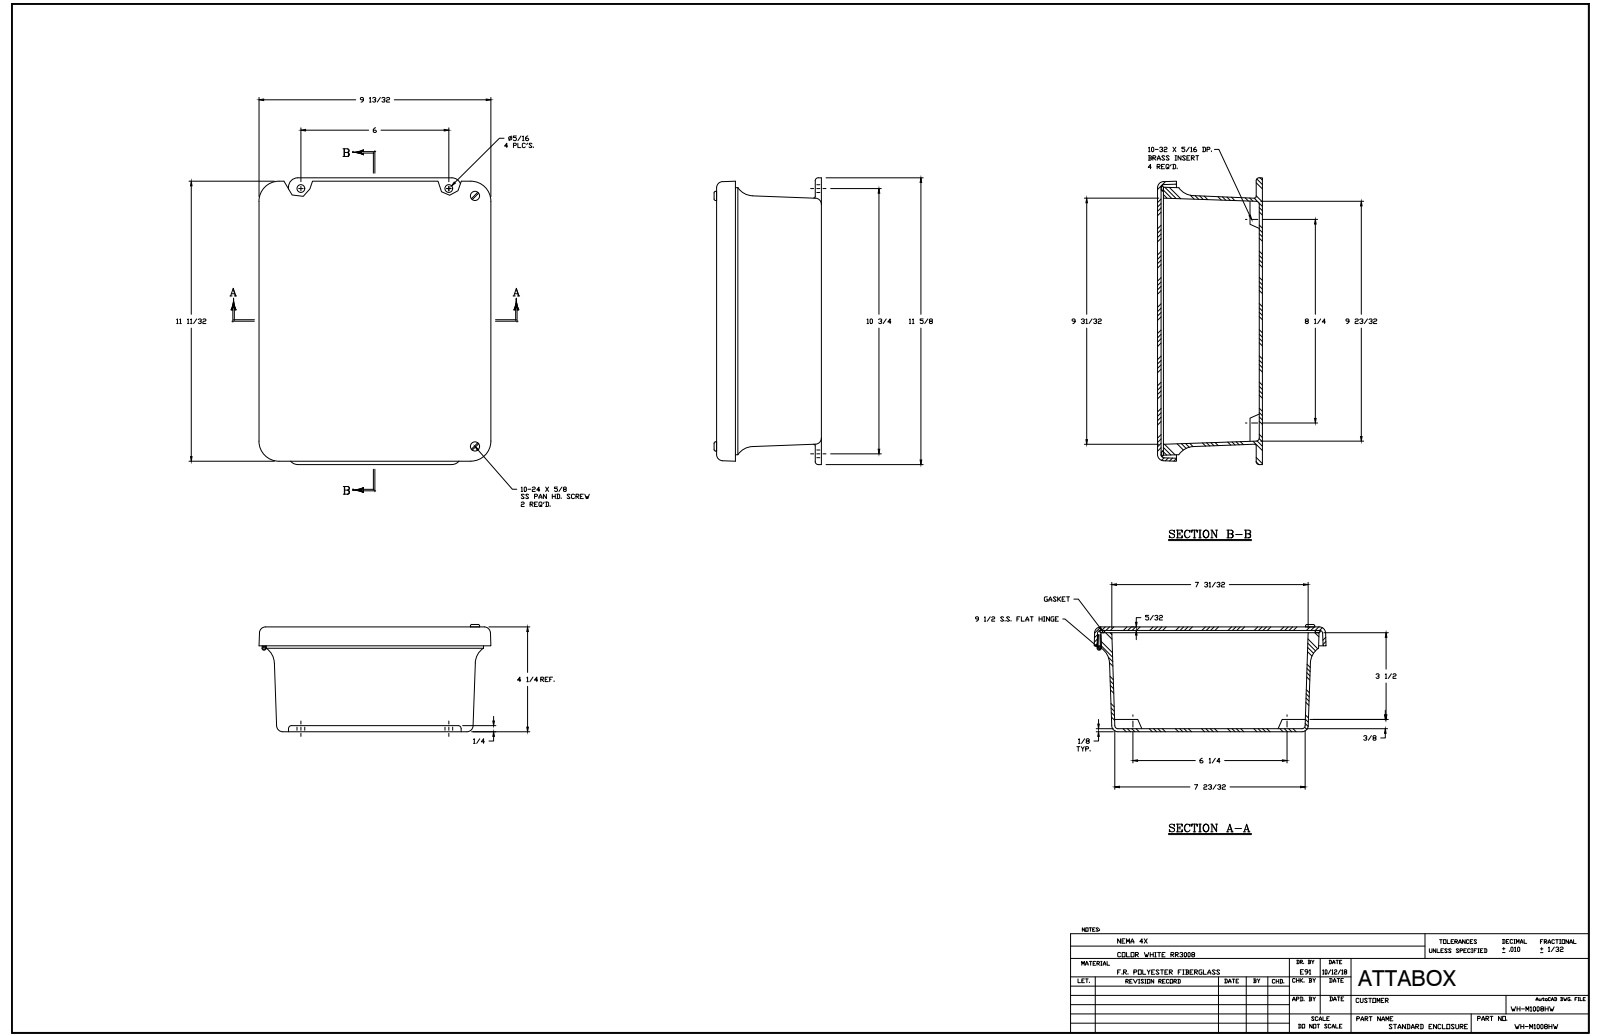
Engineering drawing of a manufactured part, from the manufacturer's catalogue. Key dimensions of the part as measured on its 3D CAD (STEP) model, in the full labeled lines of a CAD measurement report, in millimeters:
Part name (STEP PRODUCT): WH-M1008HW
STEP written by: SolidWorks 2018 (AUTOMOTIVE_DESIGN)
Units: millimetres
Bodies: 22 solids, 751 faces (259 planar, 287 cylindrical, 205 other)
Overall size (bounding box): 295.3 × 239.6 × 110.9
Volume: 992 900 mm³ · Surface area: 519 700 mm²
Round holes (diameter × count): ⌀3.3 ×8, ⌀3.6 ×8, ⌀3.9 ×5, ⌀4 ×4, ⌀5.5 ×4, ⌀3.7 ×2, ⌀2.2 ×1, ⌀2.2 ×1
Round bosses / shafts (diameter × count): ⌀6.4 ×8, ⌀6.9 ×6, ⌀3.2 ×4, ⌀3.2 ×4, ⌀4.8 ×2, ⌀4 ×2, ⌀3.9 ×1, ⌀3.9 ×1
Partial cylindrical surfaces — rounded edges, fillets, slot ends (radius × count): R0.8 ×20, R3.2 ×12, R6.4 ×8, R5.1 ×5, R9.5 ×4, R19.1 ×4, R1.6 ×2
Main face-to-face distances: 3.6, 103.9, 107.5, 3.2, 100.8, 104.4, 3, 98.8, 102, 2
Hole centre spacings: 152.4, 76.2, 6.4, 34, 63.5, 69.9, 184.2, 235
